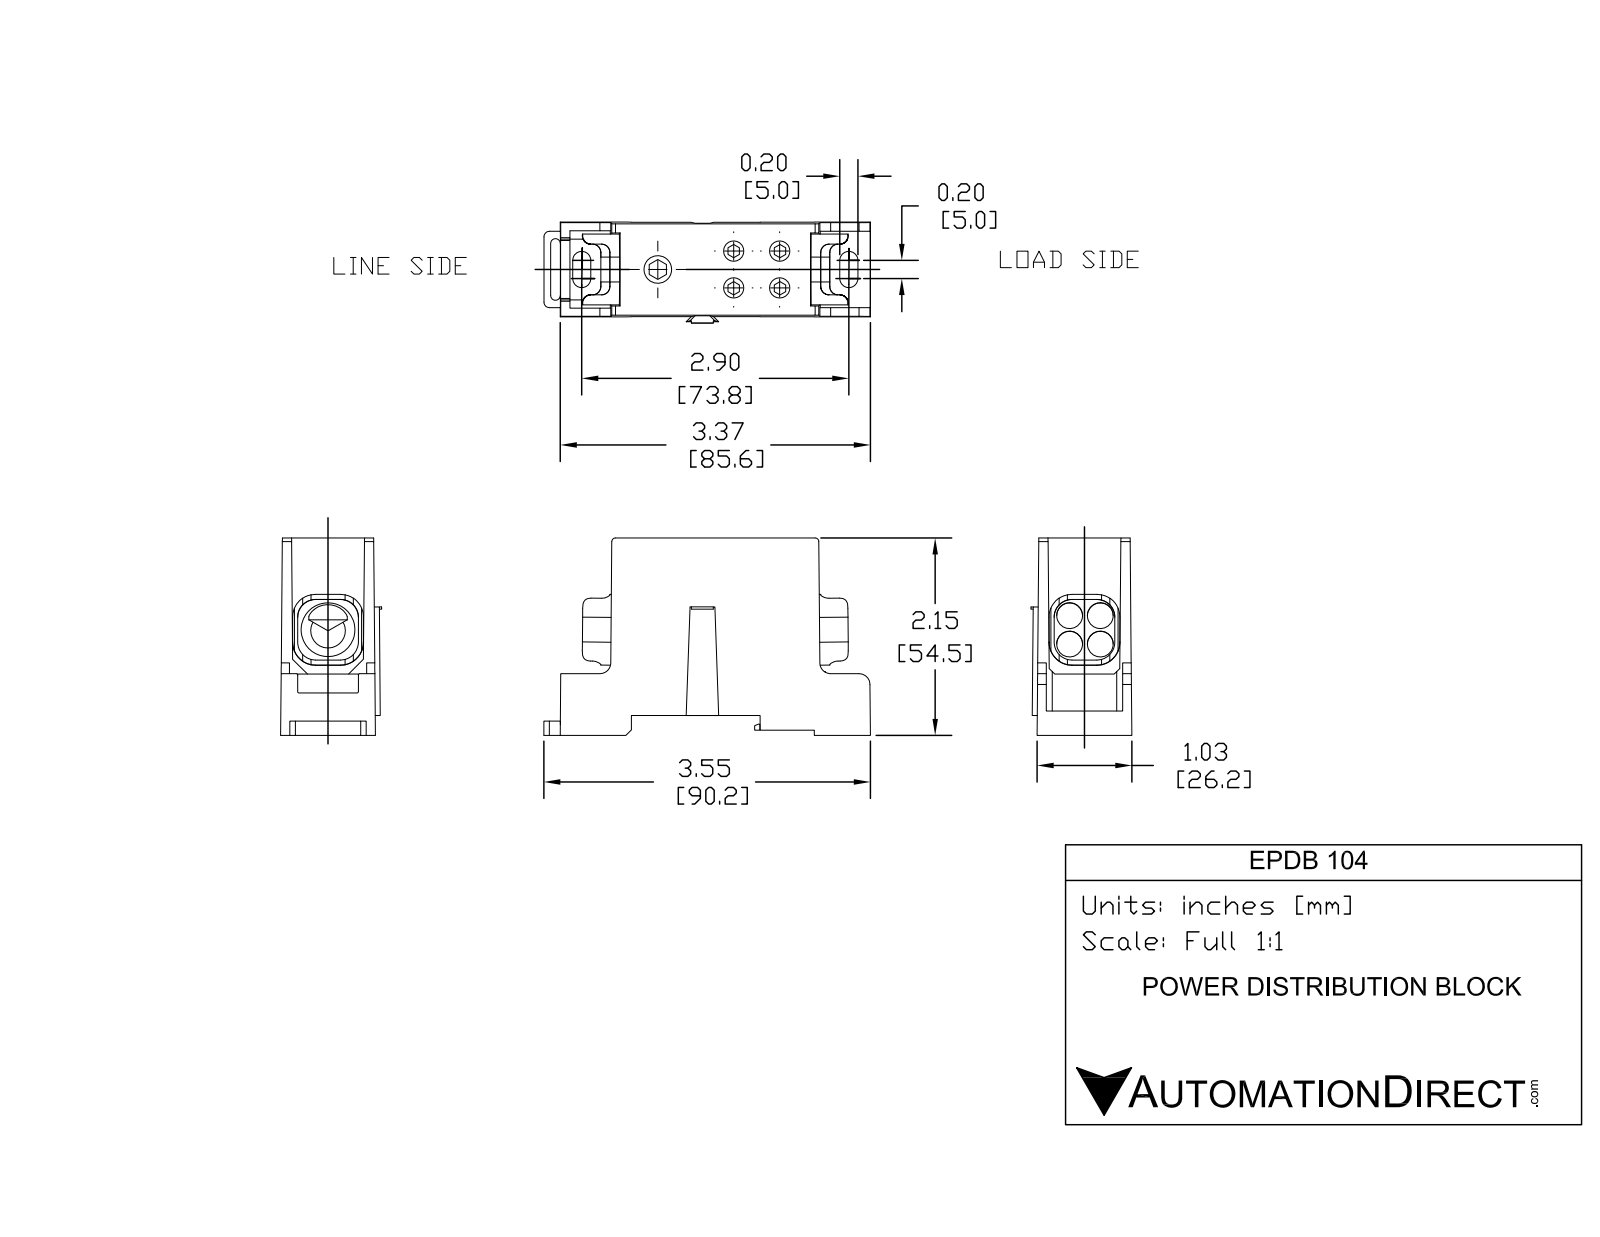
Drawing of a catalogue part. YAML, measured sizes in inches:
part_name: "EPDB104"
step_written_by: "SolidWorks 2011 (CONFIG_CONTROL_DESIGN)"
units: inches
bodies: {solids: 2, faces: 248, planar: 171, cylindrical: 73, other: 4}
overall_size: [3.549, 2.146, 1.098]
volume: 4.52
surface_area: 32.65
round_holes:
  - {diameter: 0.22, count: 4}
  - {diameter: 0.281, count: 4}
  - {diameter: 0.3, count: 1}
round_bosses_or_shafts:
  - {diameter: 0.418, count: 1}
partial_cylinders:
  - {radius: 0.09, count: 12}
  - {radius: 0.195, count: 8}
  - {radius: 0.25, count: 8}
  - {radius: 0.015, count: 4}
  - {radius: 0.099, count: 4}
  - {radius: 0.118, count: 3}
  - {radius: 0.04, count: 2}
  - {radius: 0.053, count: 2}
face_to_face_distances: [1.93, 0.216, 2.146, 0.09, 0.059, 0.631, 0.541, 0.057, 0.159, 2.089]
hole_center_spacings: [0.309, 0.334, 0.4, 0.455, 0.5, 0.64, 0.849, 1.34]
